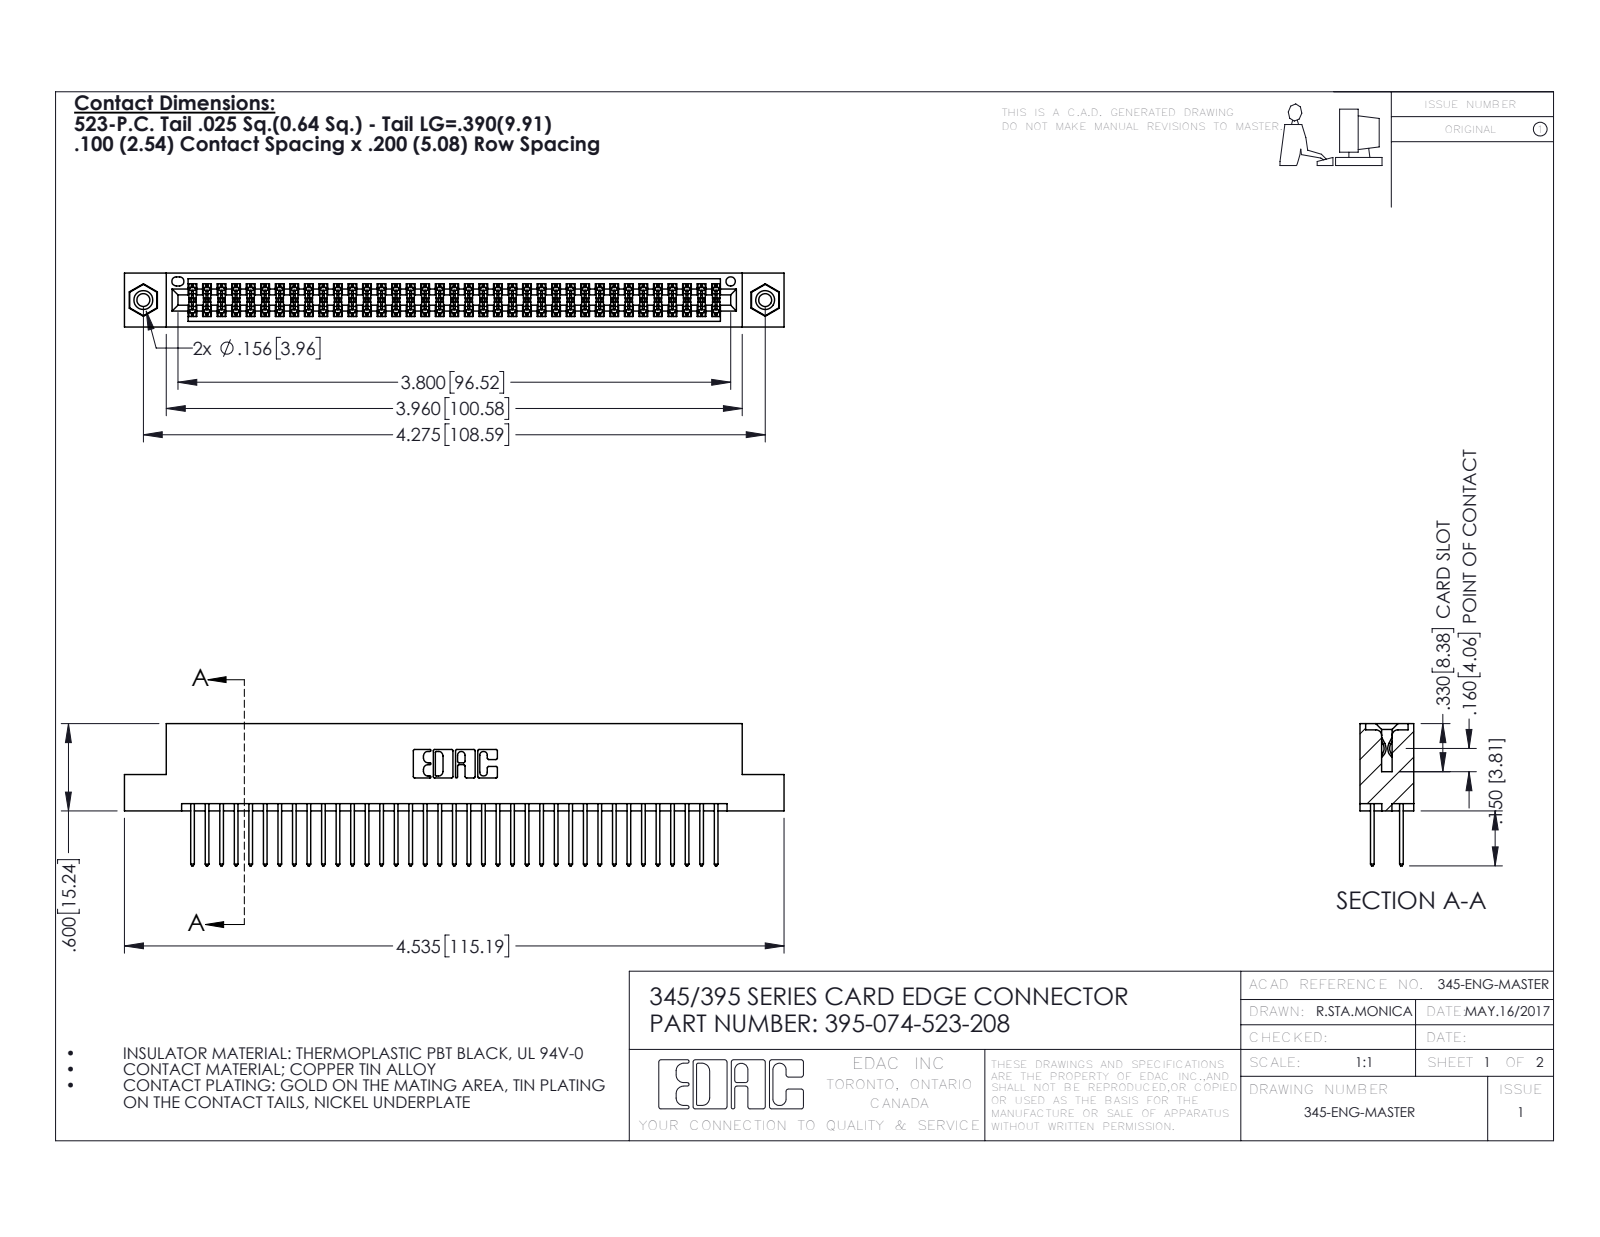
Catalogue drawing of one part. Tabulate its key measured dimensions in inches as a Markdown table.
| quantity | value |
| --- | --- |
| part name | 345-250-001_345-250-003-102; 395-074-523-208; 345 Part_Flush Mounting Lugs - 0.156 Dia-TI; 345-292-001_345-293-123 |
| STEP written by | SolidWorks 2016 (CONFIG_CONTROL_DESIGN) |
| units | inches |
| bodies | 77 solids, 3886 faces (2554 planar, 1316 cylindrical, 16 other) |
| overall size | 4.535 × 0.977 × 0.37 |
| volume | 0.689 in³ |
| surface area | 26.79 in² |
| round holes (diameter × count) | 0.089 × 2, 0.125 × 2, 0.156 × 2, 0.064 × 1 |
| round bosses / shafts (diameter × count) | 0.155 × 2 |
| partial cylindrical surfaces (radius × count) | 0.006 × 111, 0.01 × 74, 0.01 × 22, 0.007 × 6, 0.031 × 6, 0.026 × 3, 0.014 × 2, 0.019 × 2 |
| main face-to-face distances | 0.072, 0.298, 0.2, 0.098, 0.272, 0.025, 0.37, 0.225, 0.175, 0.149 |
| hole center spacings | 0.27, 4.039, 4.275 |
